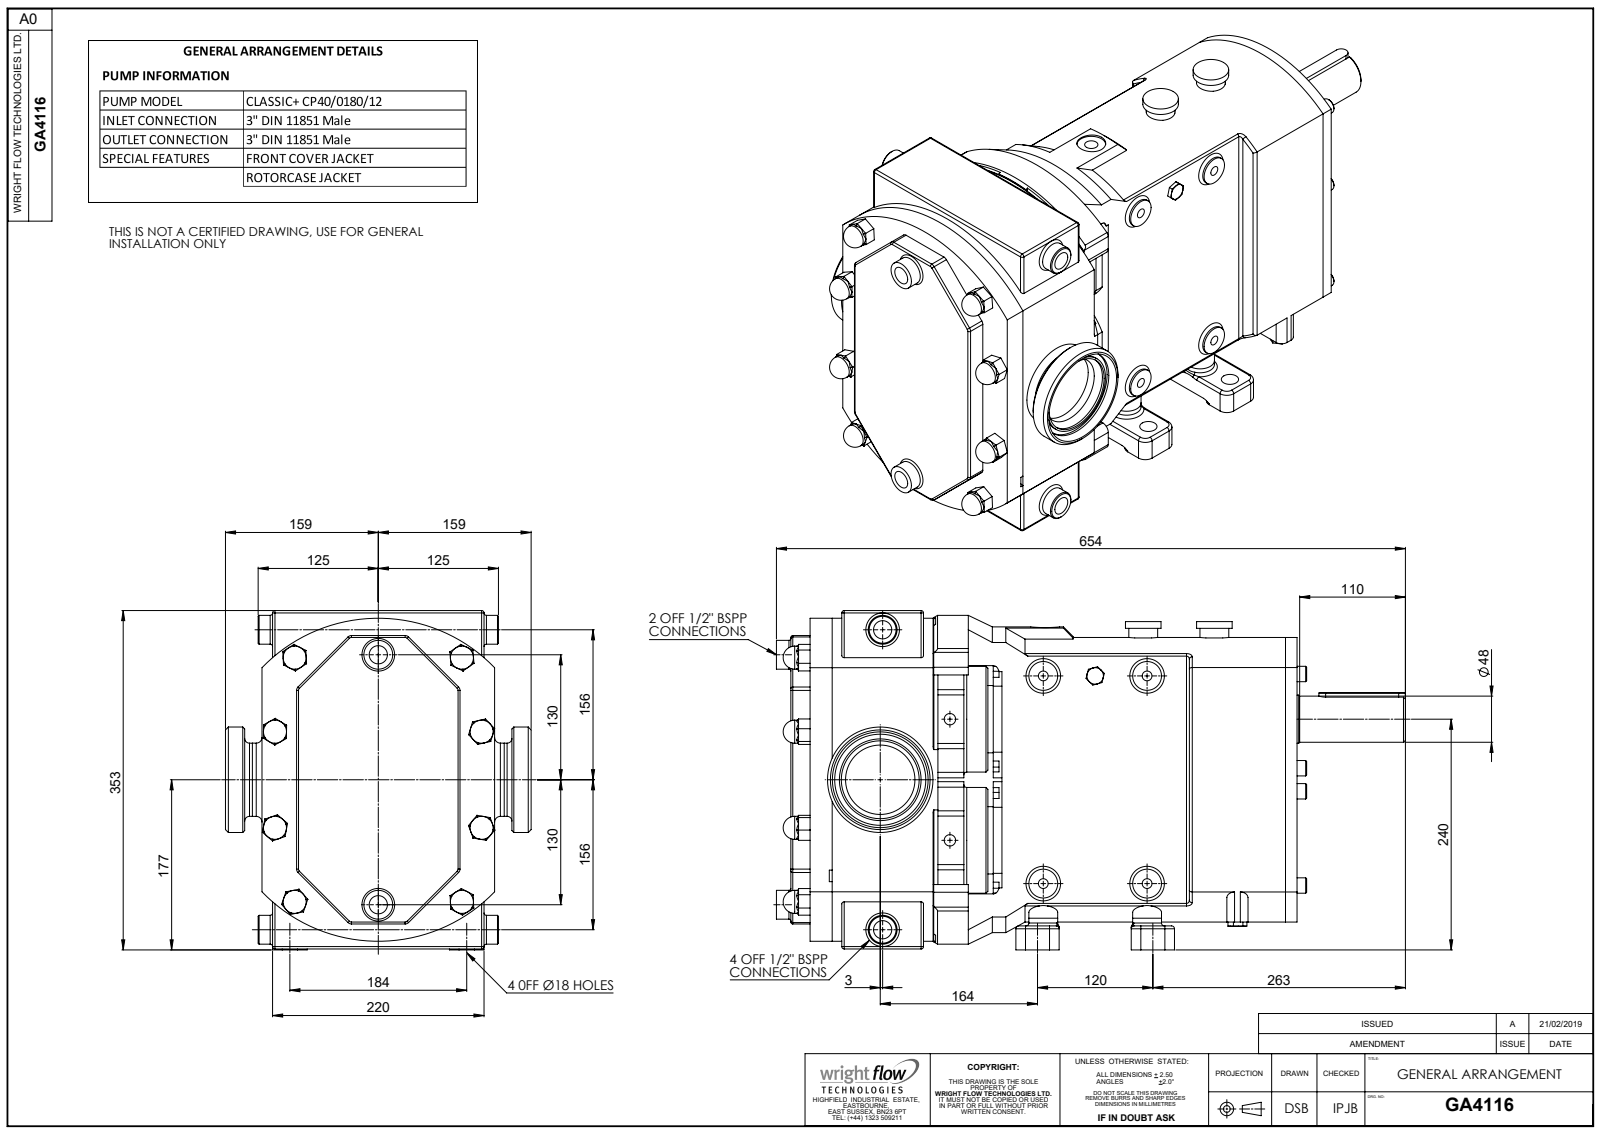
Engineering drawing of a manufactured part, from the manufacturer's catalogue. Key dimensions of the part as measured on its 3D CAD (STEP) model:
Part name (STEP PRODUCT): Copy of CP-MP40S Jacket Rotorcase^GA4116; GA4116; Copy of Z94-5031-55 - 3 INCH DIN11851^GA4116; Copy of CP40S-0180 H TSD^GA4116 (+1 more)
STEP written by: SolidWorks 2023 (AUTOMOTIVE_DESIGN)
Units: millimetres
Bodies: 6 solids, 1095 faces (401 planar, 341 cylindrical, 353 other)
Overall size (bounding box): 654.37 × 353 × 318
Volume: 28 090 000 mm³ · Surface area: 1 148 000 mm²
Round holes (diameter × count): ⌀10.2 ×4, ⌀18 ×4, ⌀18.97 ×4, ⌀11.89 ×2, ⌀35 ×2, ⌀13.83 ×1, ⌀30 ×1, ⌀72.2 ×1, ⌀81 ×1, ⌀94.8 ×1
Round bosses / shafts (diameter × count): ⌀30 ×14, ⌀24 ×8, ⌀16 ×6, ⌀110 ×2, ⌀70 ×2, ⌀37 ×2, ⌀31.75 ×2, ⌀250 ×1
Partial cylindrical surfaces — rounded edges, fillets, slot ends (radius × count): R10 ×24, R3 ×22, R8 ×20, R2.5 ×12, R5 ×12, R6 ×10, R2 ×8, R11 ×4
Main face-to-face distances: 21, 161, 30, 51, 191, 212, 140, 506.62, 526.62, 20
Hole centre spacings: 92.35, 92.54, 96.05, 107.04, 108, 112.07, 116.4, 120
